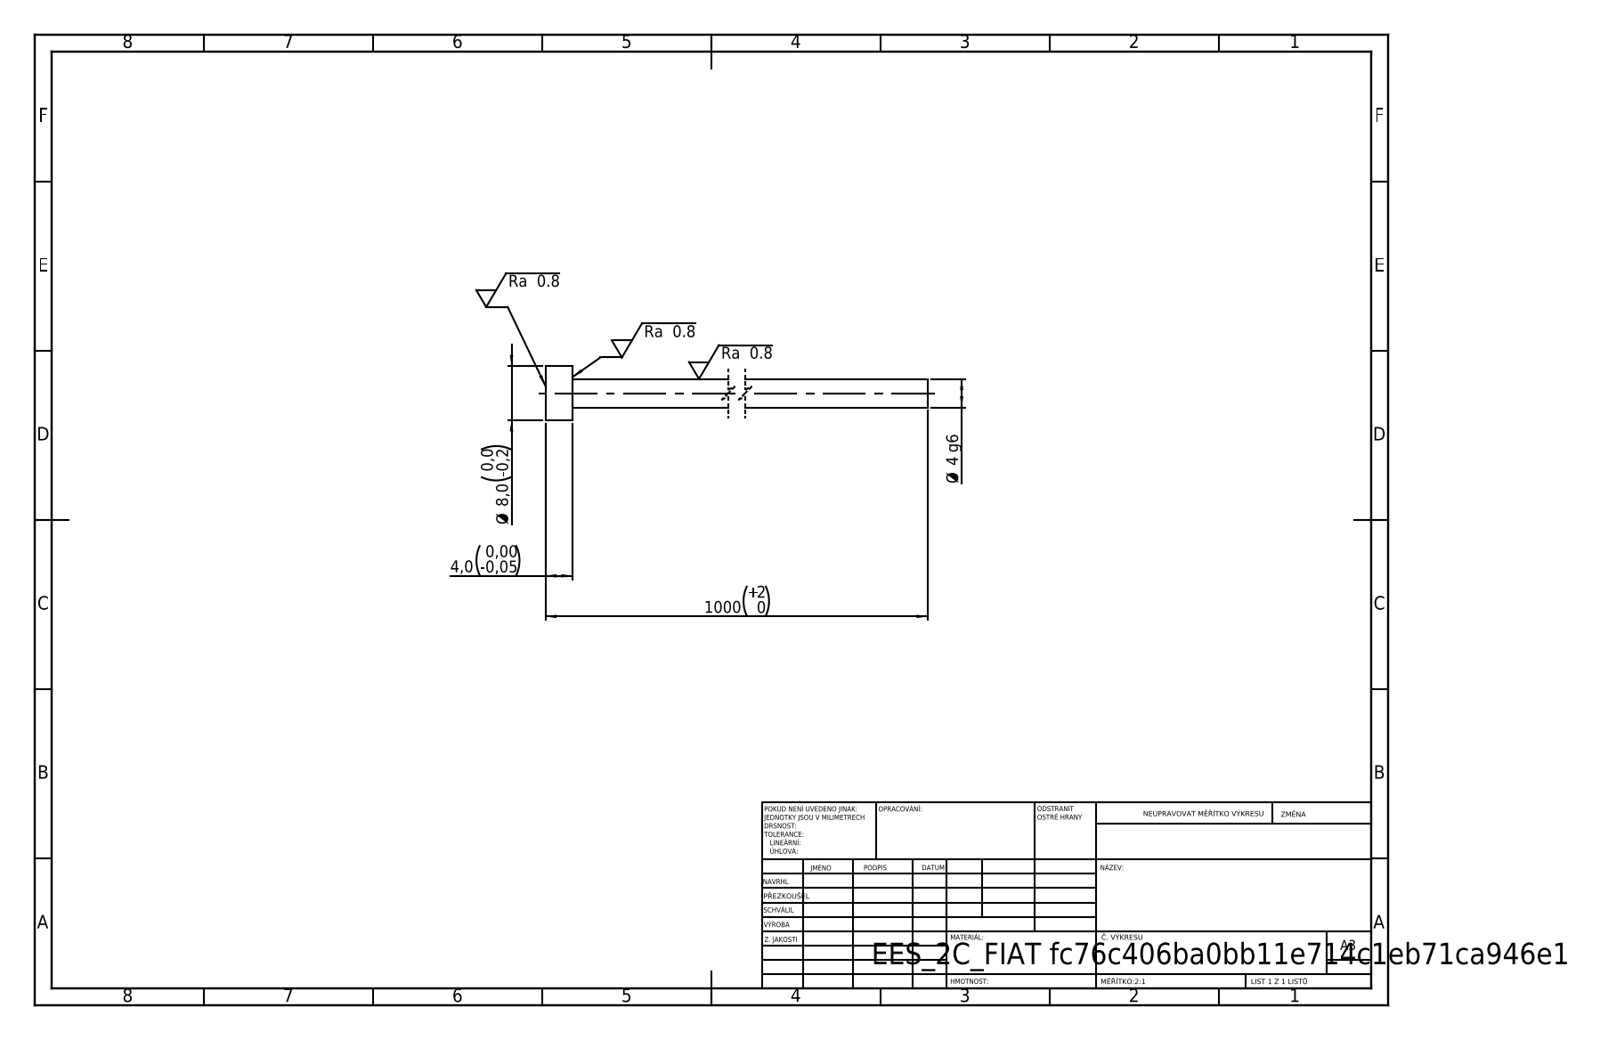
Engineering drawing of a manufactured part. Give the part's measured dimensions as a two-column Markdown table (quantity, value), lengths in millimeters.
| quantity | value |
| --- | --- |
| STEP written by | SolidWorks 2019 (CONFIG_CONTROL_DESIGN) |
| units | millimeters |
| bodies | 1 solid, 7 faces (3 planar, 4 cylindrical, 0 other) |
| overall size | 1000 × 8 × 8 |
| volume | 14 000 mm³ |
| surface area | 13 343 mm² |
| round bosses / shafts (diameter × count) | 8 × 1, 4.2 × 1 |
| main face-to-face distances | 4, 1000, 996 |
